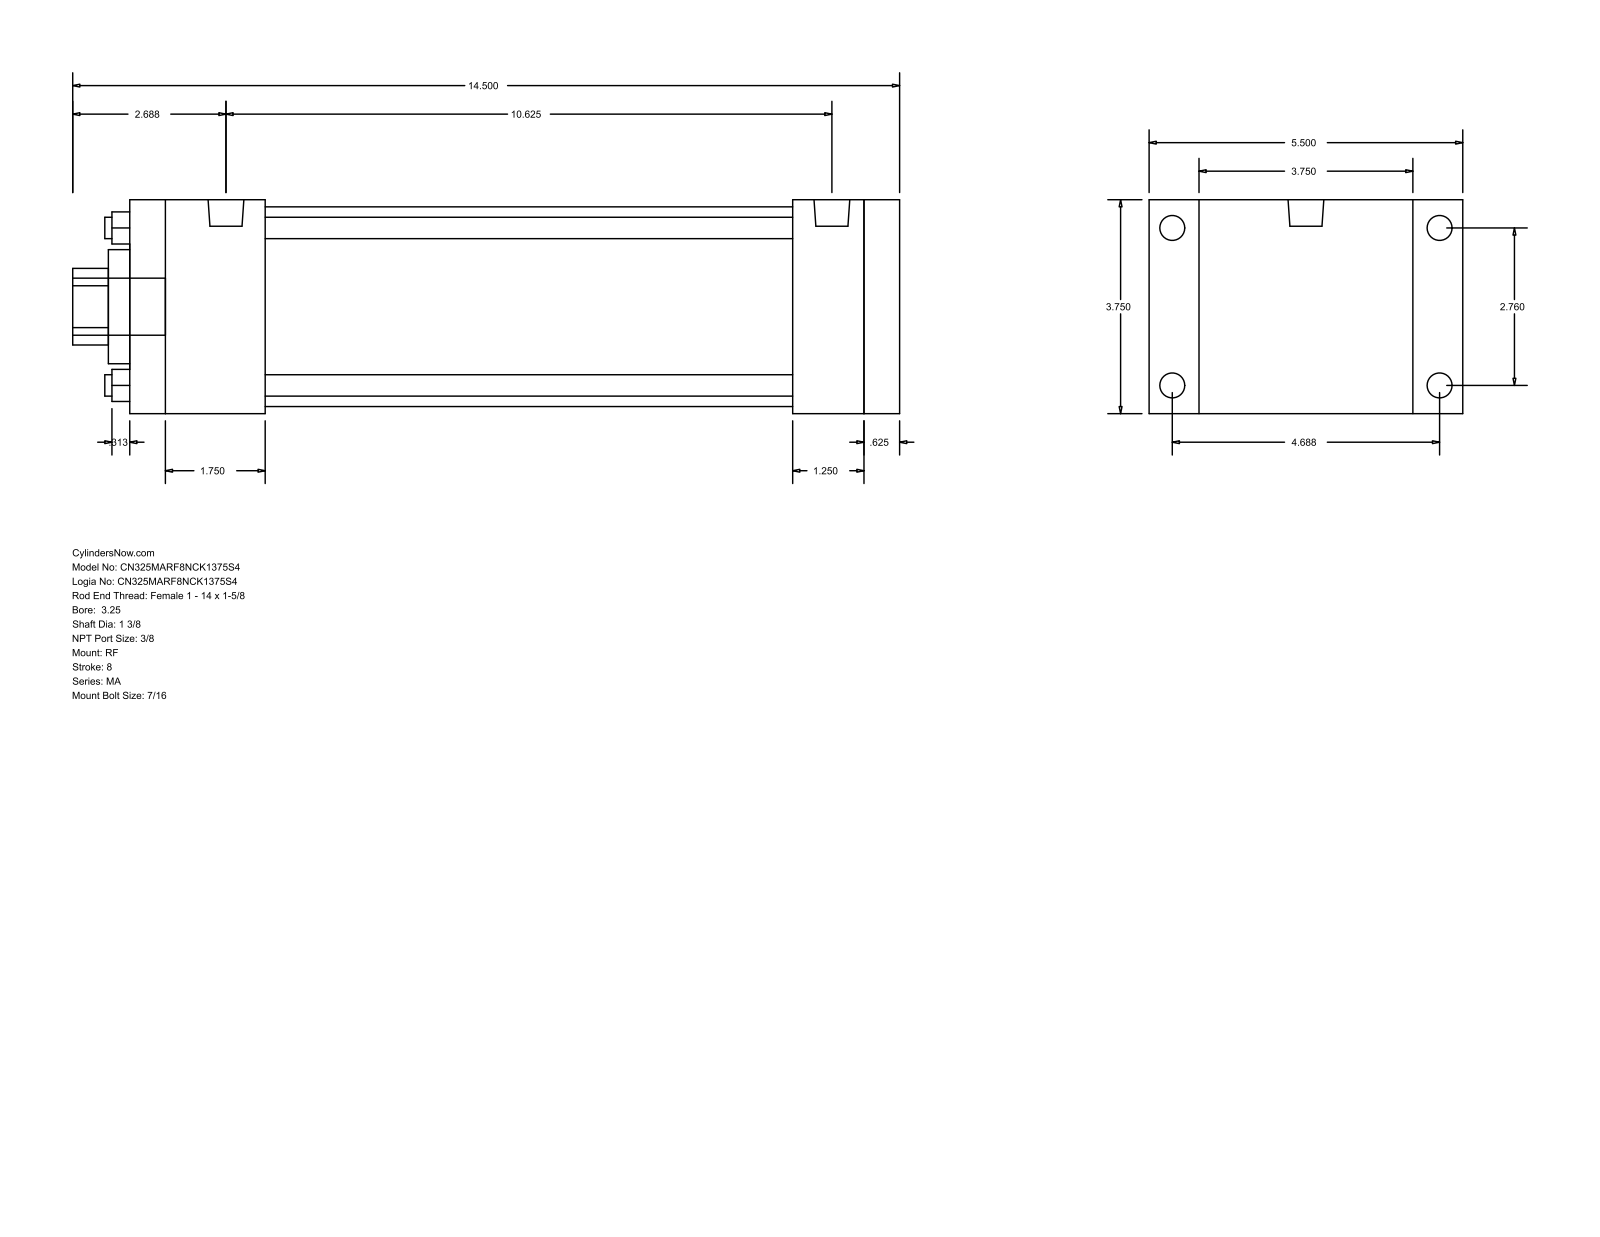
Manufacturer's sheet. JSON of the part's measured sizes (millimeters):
{"part_name": "MA_RF__0325_1.375", "step_written_by": "GSSL Pune (CONFIG_CONTROL_DESIGN)", "units": "millimeters", "bodies": {"solids": 0, "faces": 92, "planar": 64, "cylindrical": 28, "other": 0}, "overall_size": [368.3, 139.7, 95.25], "round_holes": [[9.53, 4], [34.92, 1], [50.8, 1], [88.9, 1]], "round_bosses_or_shafts": [[11.11, 8], [15.93, 2], [25.4, 1]], "partial_cylinders_radius": [[17.06, 1]], "face_to_face_distances": [95.24, 342.9, 15.87, 327.03, 22.23, 117.47, 295.28, 31.75, 47.62, 60.32], "hole_center_spacings": [49.57, 70.1, 99.14]}
